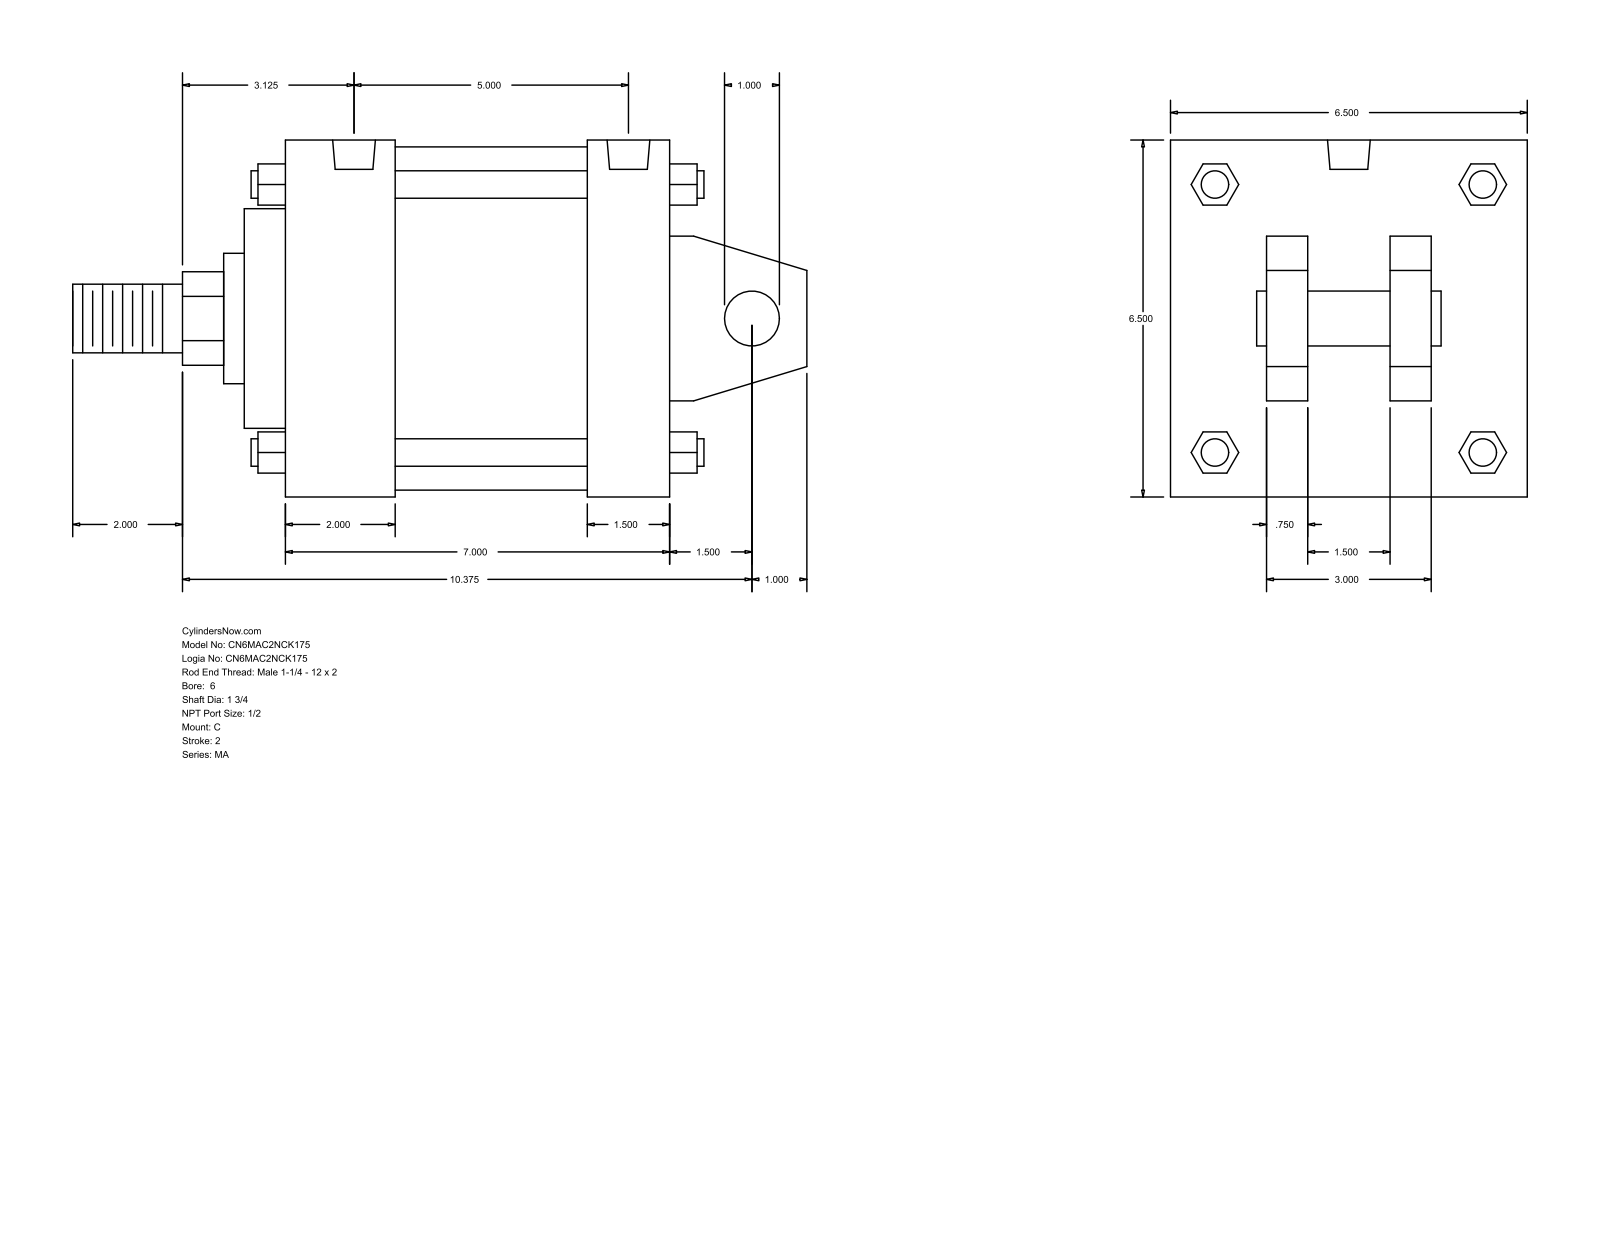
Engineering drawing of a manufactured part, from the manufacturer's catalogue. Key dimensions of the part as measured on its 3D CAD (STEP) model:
Part name (STEP PRODUCT): MA_C__0600_1.75
STEP written by: GSSL Pune (CONFIG_CONTROL_DESIGN)
Units: millimetres
Bodies: 0 solids, 141 faces (109 planar, 32 cylindrical, 0 other)
Overall size (bounding box): 339.73 × 165.1 × 165.1
Round holes (diameter × count): ⌀17.46 ×4, ⌀19.77 ×2
Round bosses / shafts (diameter × count): ⌀12.7 ×4, ⌀158.75 ×1, ⌀101.6 ×1, ⌀60.33 ×1, ⌀44.45 ×1, ⌀31.75 ×1, ⌀25.4 ×1
Partial cylindrical surfaces — rounded edges, fillets, slot ends (radius × count): R21.63 ×1
Main face-to-face distances: 165.1, 177.81, 19.05, 63.5, 101.6, 50.8, 44.45, 120.65, 139.7, 57.15
Hole centre spacings: 127
